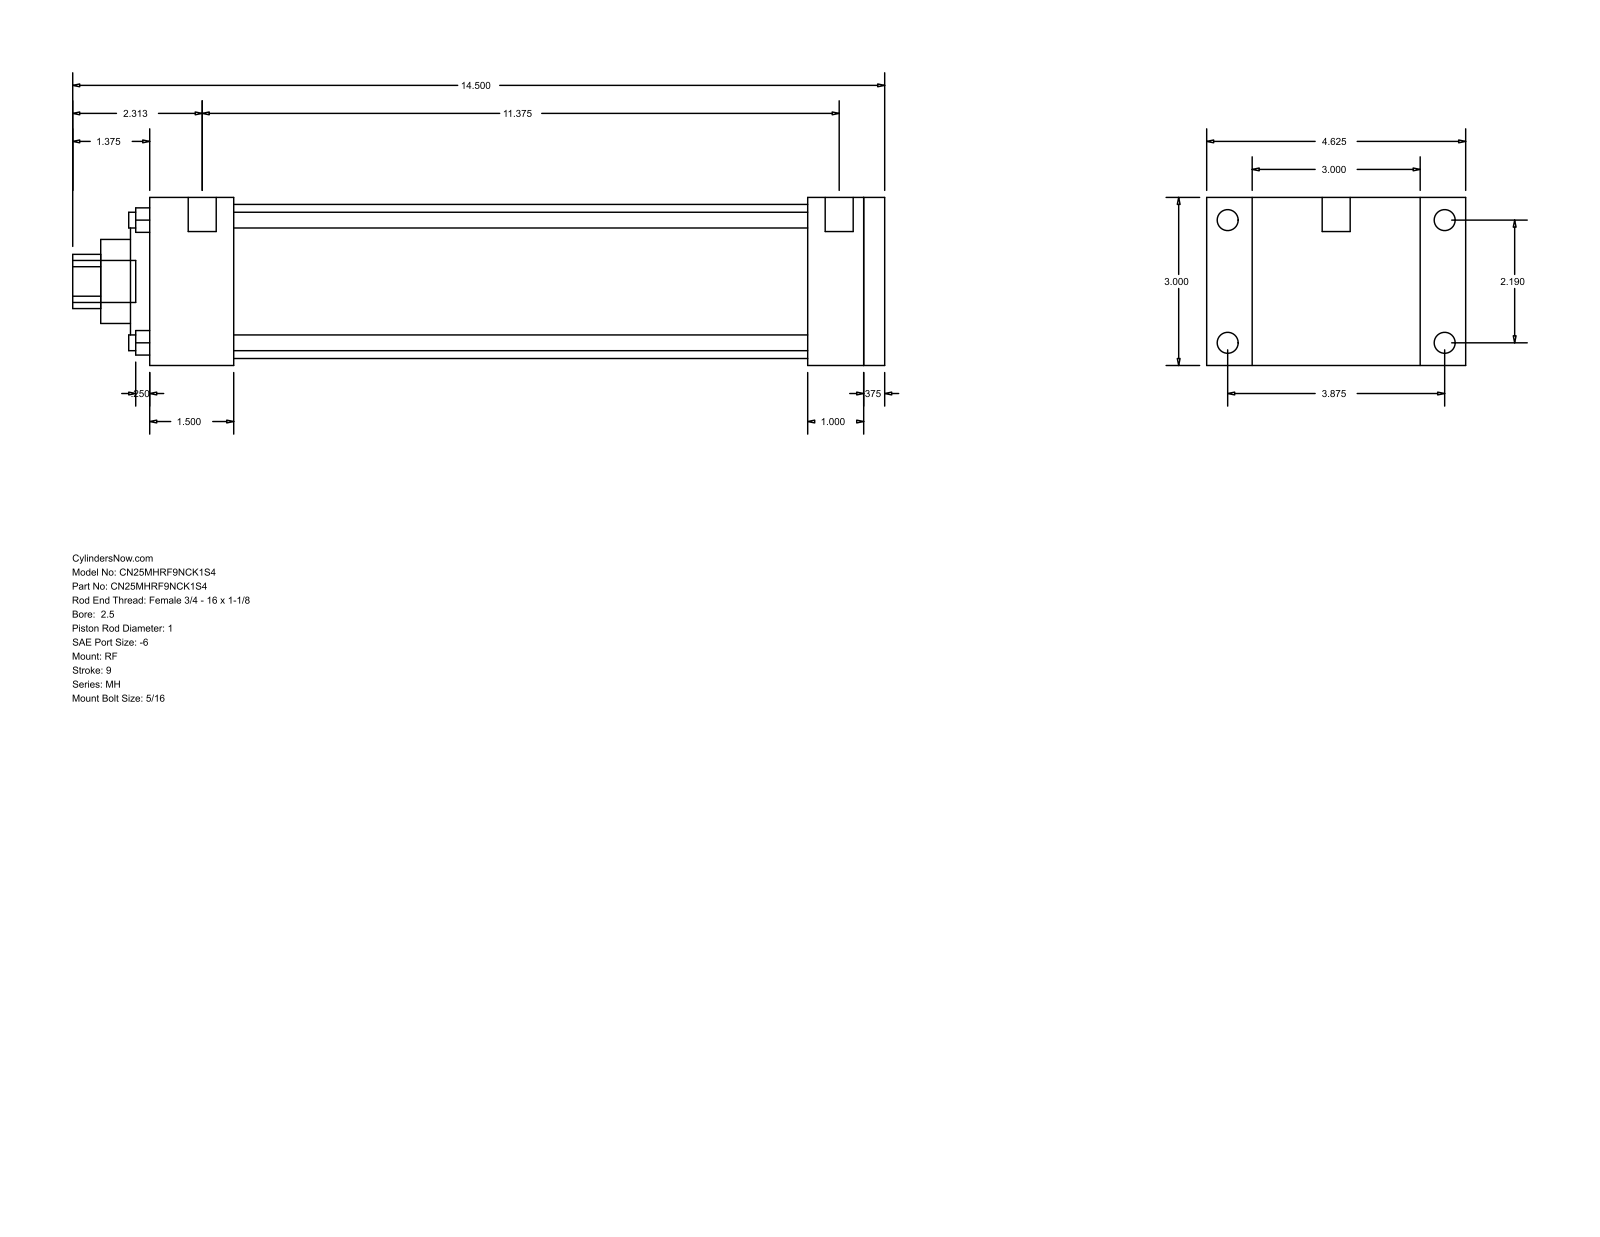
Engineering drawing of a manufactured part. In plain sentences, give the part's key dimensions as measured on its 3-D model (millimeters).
The part is named "MH_RF__0250_1". Its 3-D file was written by "GSSL Pune (CONFIG_CONTROL_DESIGN)". It is 0 solids with 94 faces: 65 planar, 29 cylindrical and 0 other. Overall it measures 368.3 by 117.47 by 76.2 millimeters. Round holes: 4 of diameter 7.14, 1 of diameter 25.4, 1 of diameter 38.1, 1 of diameter 60.33, 1 of diameter 69.85. Round bosses or shafts: 4 of diameter 9.53, 4 of diameter 5.56, 2 of diameter 12.7, 1 of diameter 19.05. Partial cylindrical surfaces (rounded edges, fillets, slot ends): 1 of radius 12.29. The main face-to-face distances are 76.2, 9.53, 333.38, 323.85, 34.92, 25.39, 298.46, 38.11, 260.35, 285.74. The hole center spacings are 39.33, 55.62, 78.66.
